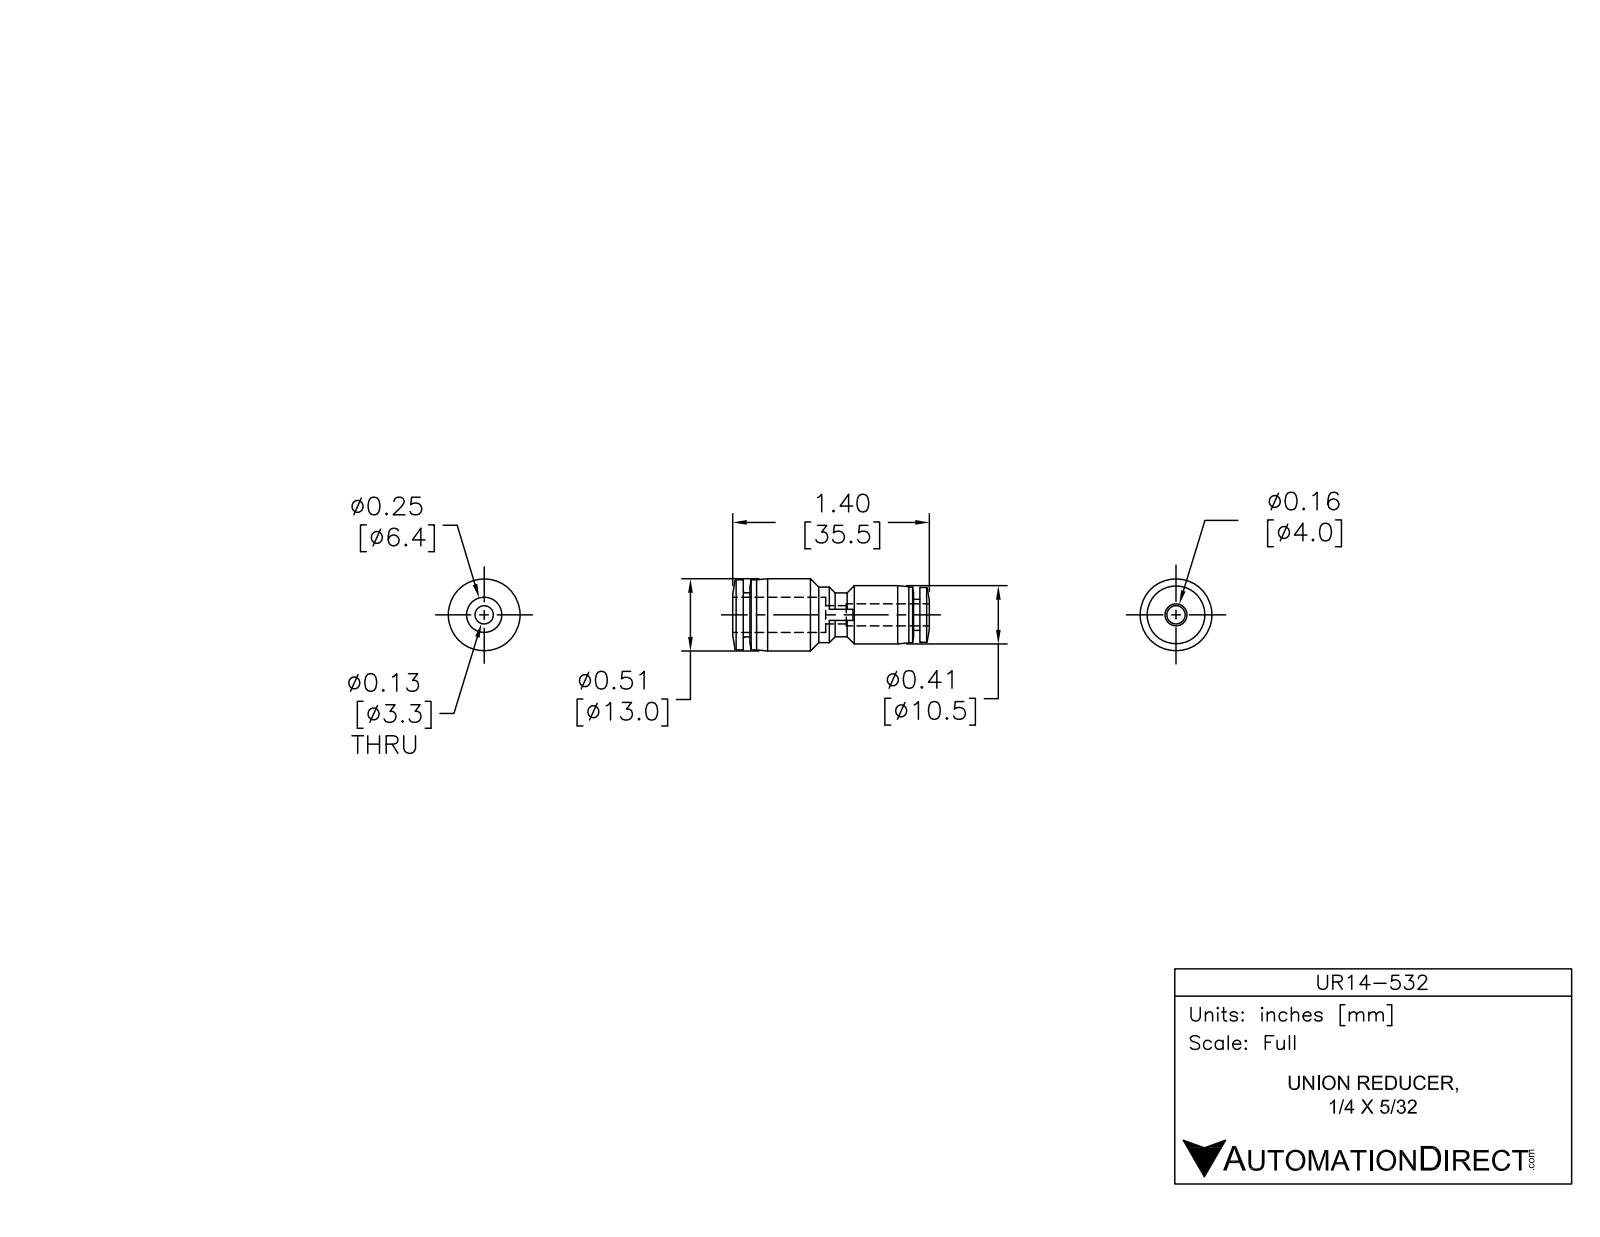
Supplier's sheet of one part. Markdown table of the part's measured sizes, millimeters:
| quantity | value |
| --- | --- |
| part name | UR14-532 |
| STEP written by | SolidWorks 2015 (AUTOMOTIVE_DESIGN) |
| units | millimeters |
| bodies | 1 solid, 69 faces (11 planar, 26 cylindrical, 32 other) |
| overall size | 35.4 × 13 × 13 |
| volume | 2 510 mm³ |
| surface area | 2 235 mm² |
| round holes (diameter × count) | 3.2 × 1, 4.3 × 1, 6.6 × 1 |
| round bosses / shafts (diameter × count) | 13 × 1, 12.6 × 1, 10.5 × 1, 10 × 1, 9.9 × 1, 8 × 1, 7.9 × 1, 5.6 × 1 |
| main face-to-face distances | 31.8, 30.6, 1.2, 14.9, 16.9, 13.7, 1.1, 15.7, 29.4, 30.7 |
